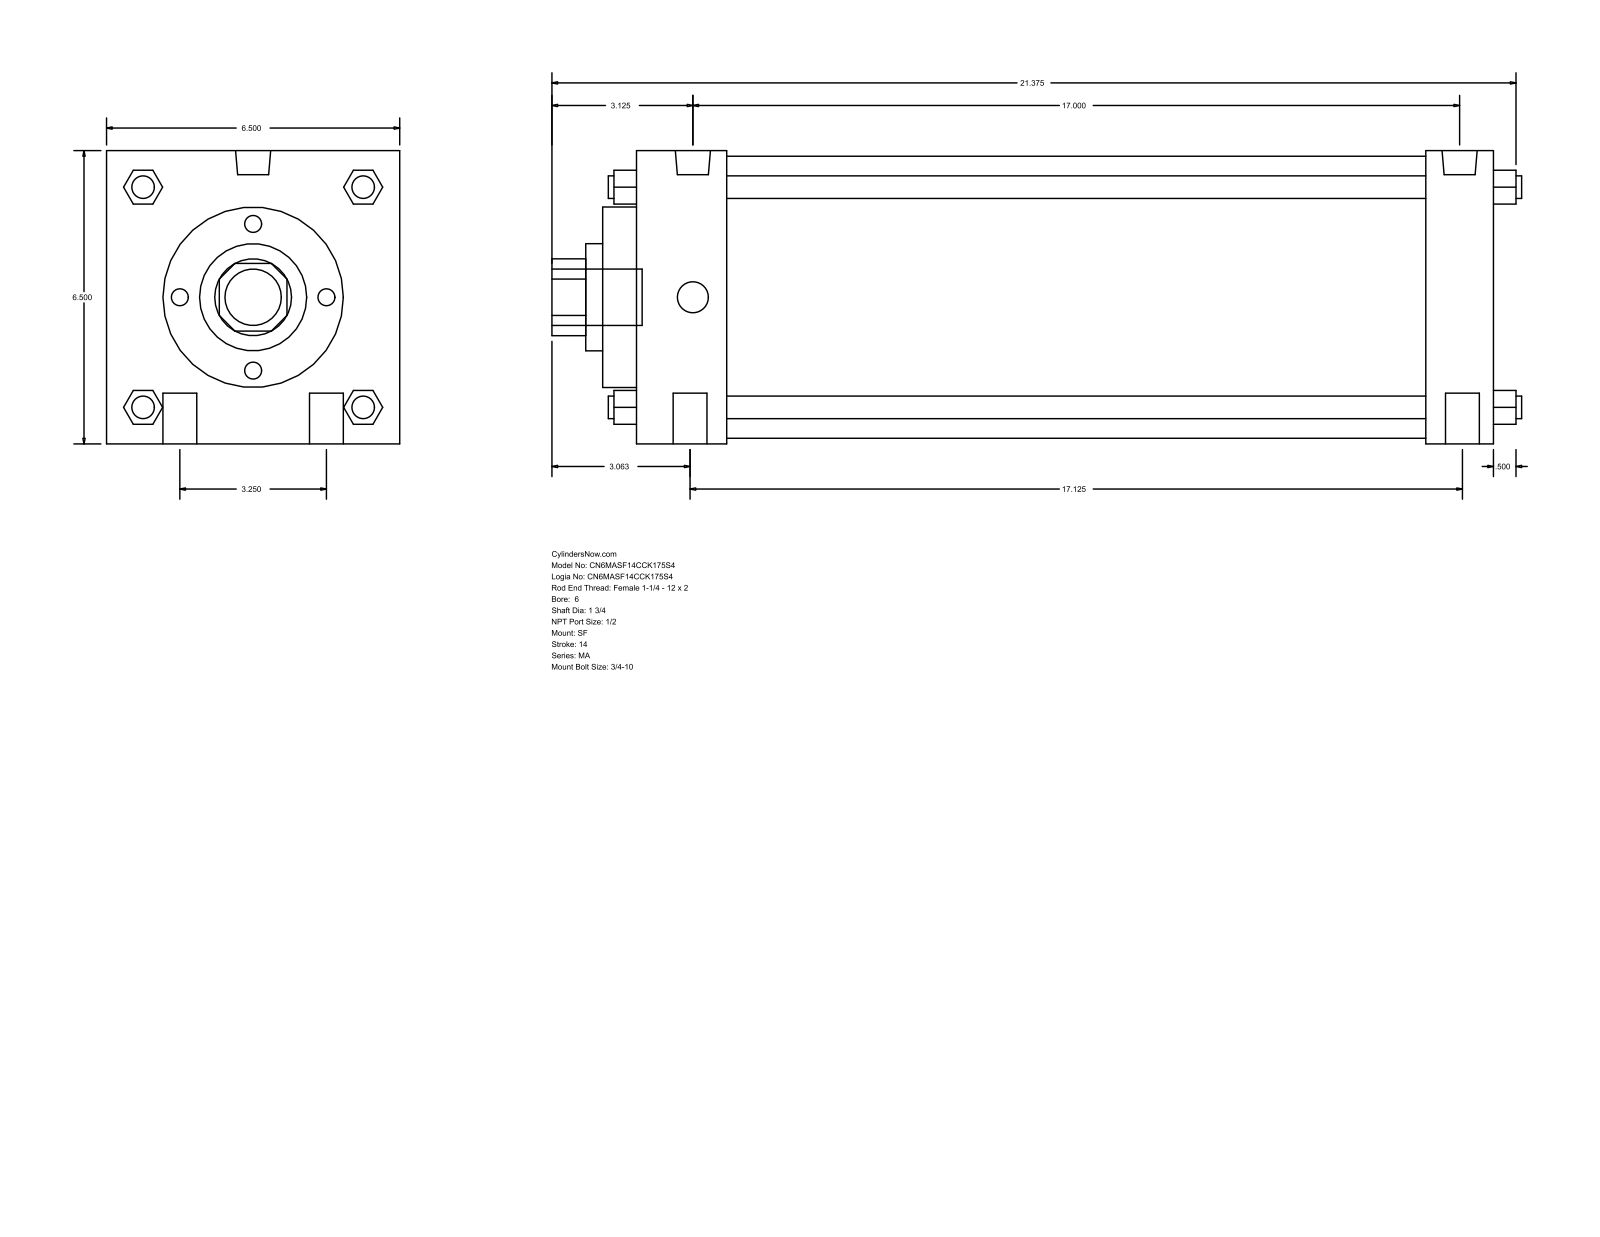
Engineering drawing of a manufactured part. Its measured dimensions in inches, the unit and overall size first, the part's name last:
Units: inches
Overall size (bounding box): 21.5 × 6.5 × 6.5
Round holes (diameter × count): ⌀1.75 ×1, ⌀2.375 ×1, ⌀4 ×1, ⌀6.25 ×1
Round bosses / shafts (diameter × count): ⌀0.75 ×4, ⌀0.5 ×4, ⌀0.778 ×2, ⌀0.687 ×2, ⌀1.25 ×1
Partial cylindrical surfaces — rounded edges, fillets, slot ends (radius × count): R0.852 ×1
Main face-to-face distances: 6.5, 19, 0.75, 2, 17.5, 1.5, 15.5, 17, 2.75, 18.25
Bodies: 0 solids, 126 faces (95 planar, 31 cylindrical, 0 other)
Part name (STEP PRODUCT): MA_SF__0600_1.75
STEP written by: GSSL Pune (CONFIG_CONTROL_DESIGN)
